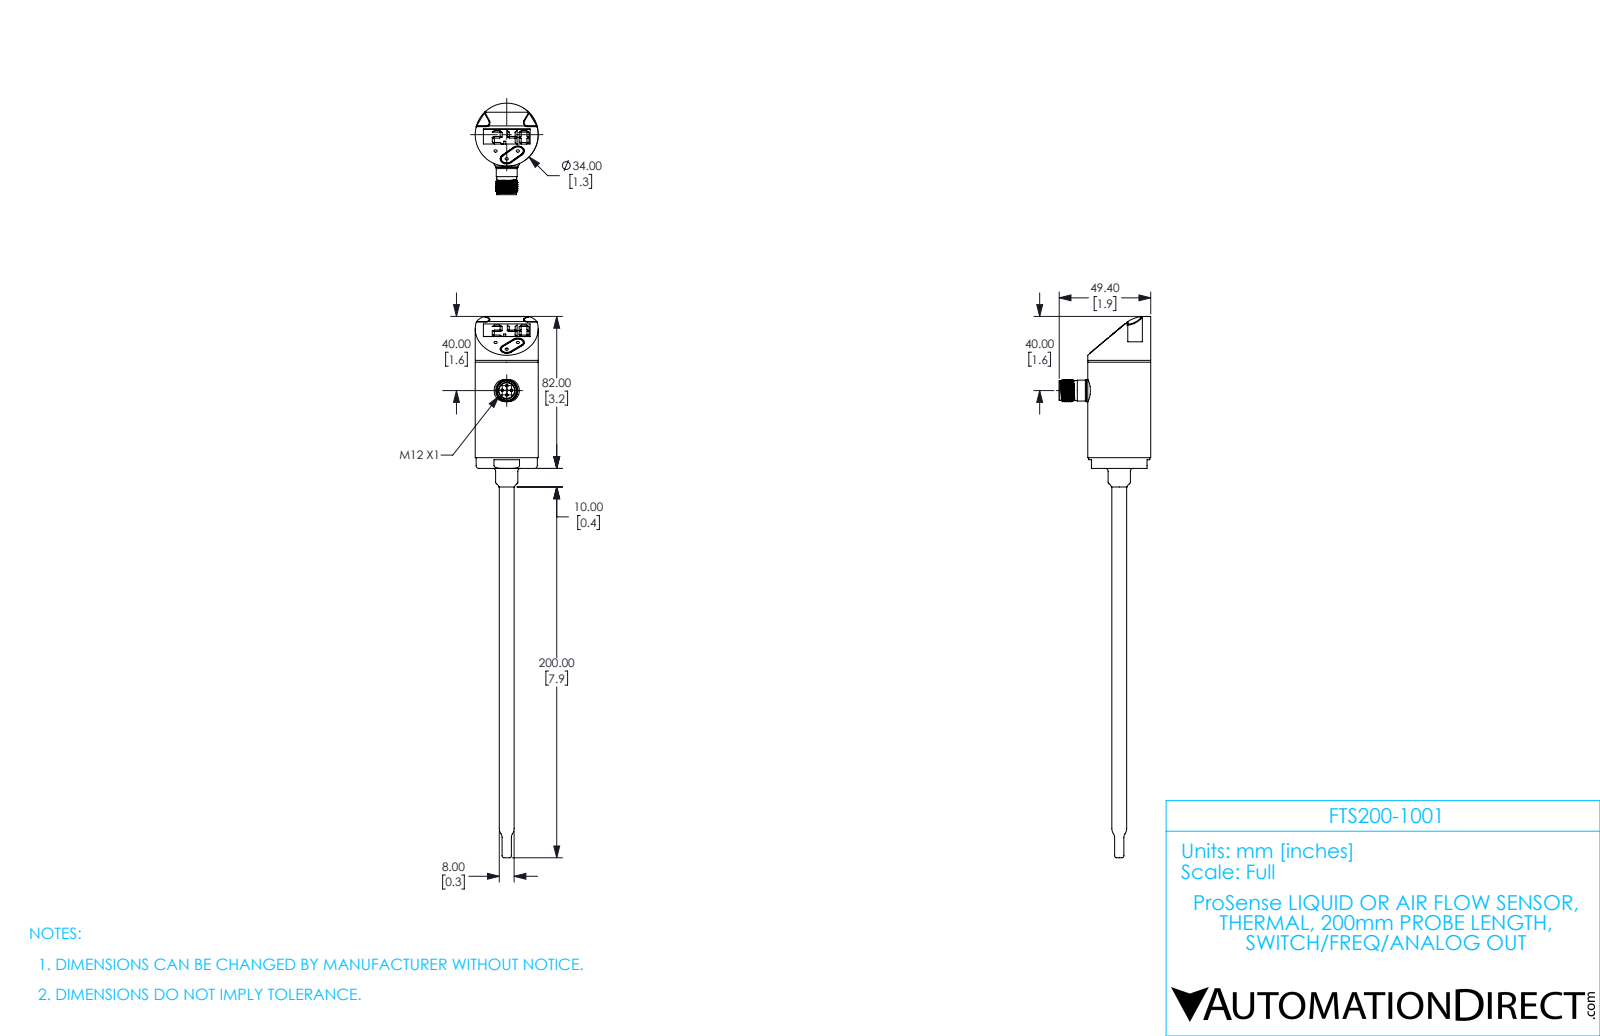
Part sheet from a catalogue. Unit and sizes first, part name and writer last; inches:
Units: inches
Overall size (bounding box): 11.496 × 1.945 × 1.339
Round holes (diameter × count): ⌀0.333 ×1
Round bosses / shafts (diameter × count): ⌀0.055 ×4, ⌀0.039 ×4, ⌀0.472 ×2, ⌀1.339 ×1, ⌀1.331 ×1, ⌀1.299 ×1, ⌀0.445 ×1, ⌀0.425 ×1
Partial cylindrical surfaces — rounded edges, fillets, slot ends (radius × count): R0.071 ×2, R0.087 ×2, R0.118 ×2, R0.138 ×2, R0.591 ×2, R0.268 ×1, R0.984 ×1
Main face-to-face distances: 1.287, 1.181, 0.106, 1.441, 0.26, 0.154, 0.228, 3.228, 3, 0.185
Volume: 4.808 in³ · Surface area: 25.61 in²
Bodies: 2 solids, 326 faces (184 planar, 77 cylindrical, 65 other)
Part name (STEP PRODUCT): FTS200
STEP written by: SolidWorks 2017 (AUTOMOTIVE_DESIGN)
